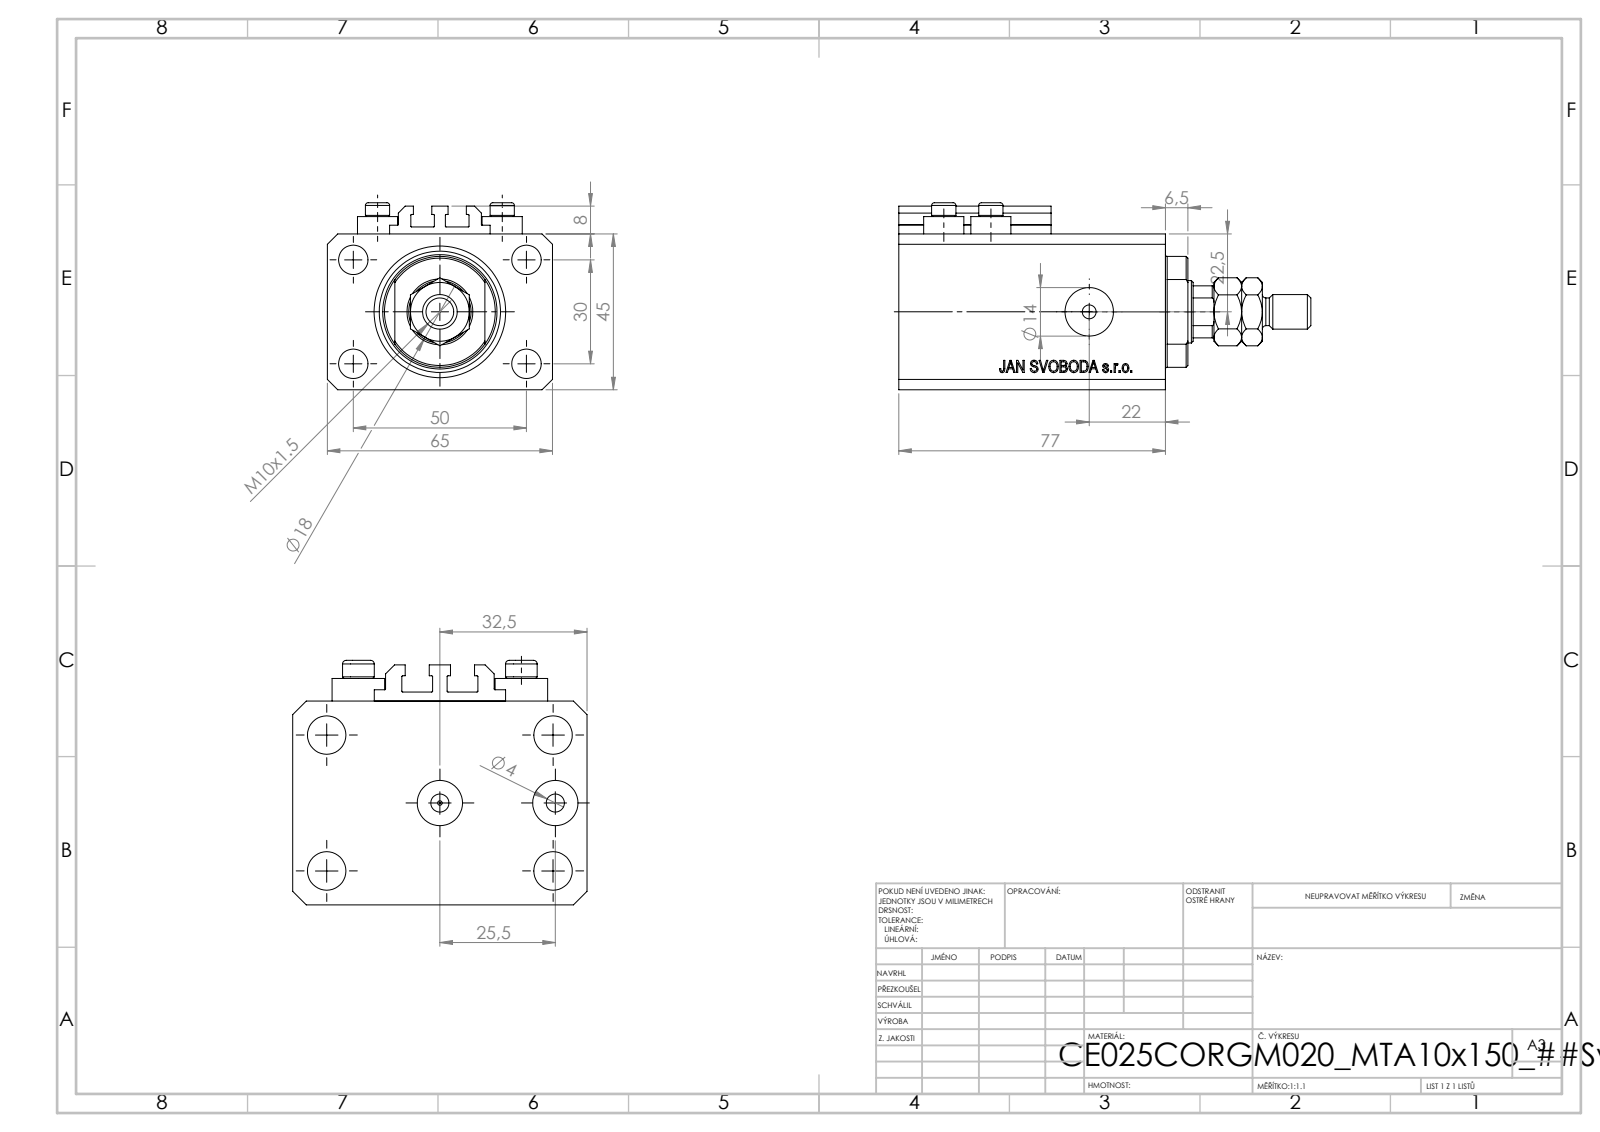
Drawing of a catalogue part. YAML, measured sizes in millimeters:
part_name: "ALLEN BOLT V250CE; MTA; V250CE_VC_C; V250CE_C_VCP (+1 more)"
step_written_by: "SolidWorks 2019 (CONFIG_CONTROL_DESIGN)"
units: millimeters
bodies: {solids: 9, faces: 1091, planar: 519, cylindrical: 96, other: 476}
overall_size: [119, 65, 54]
volume: 215987
surface_area: 59418
round_holes:
  - {diameter: 4, count: 8}
  - {diameter: 8.5, count: 5}
  - {diameter: 10, count: 2}
  - {diameter: 14, count: 2}
  - {diameter: 1.25, count: 1}
  - {diameter: 18, count: 1}
  - {diameter: 25, count: 1}
  - {diameter: 38, count: 1}
round_bosses_or_shafts:
  - {diameter: 11.6, count: 4}
  - {diameter: 7, count: 4}
  - {diameter: 8, count: 1}
partial_cylinders:
  - {radius: 0.2, count: 10}
  - {radius: 8.5, count: 1}
  - {radius: 16, count: 1}
face_to_face_distances: [45, 65, 14, 77, 63, 6.9, 56.1, 70.1, 20.5, 3]
hole_center_spacings: [29.15, 13.6, 15.01, 30, 36, 38.48, 50, 52.68]
